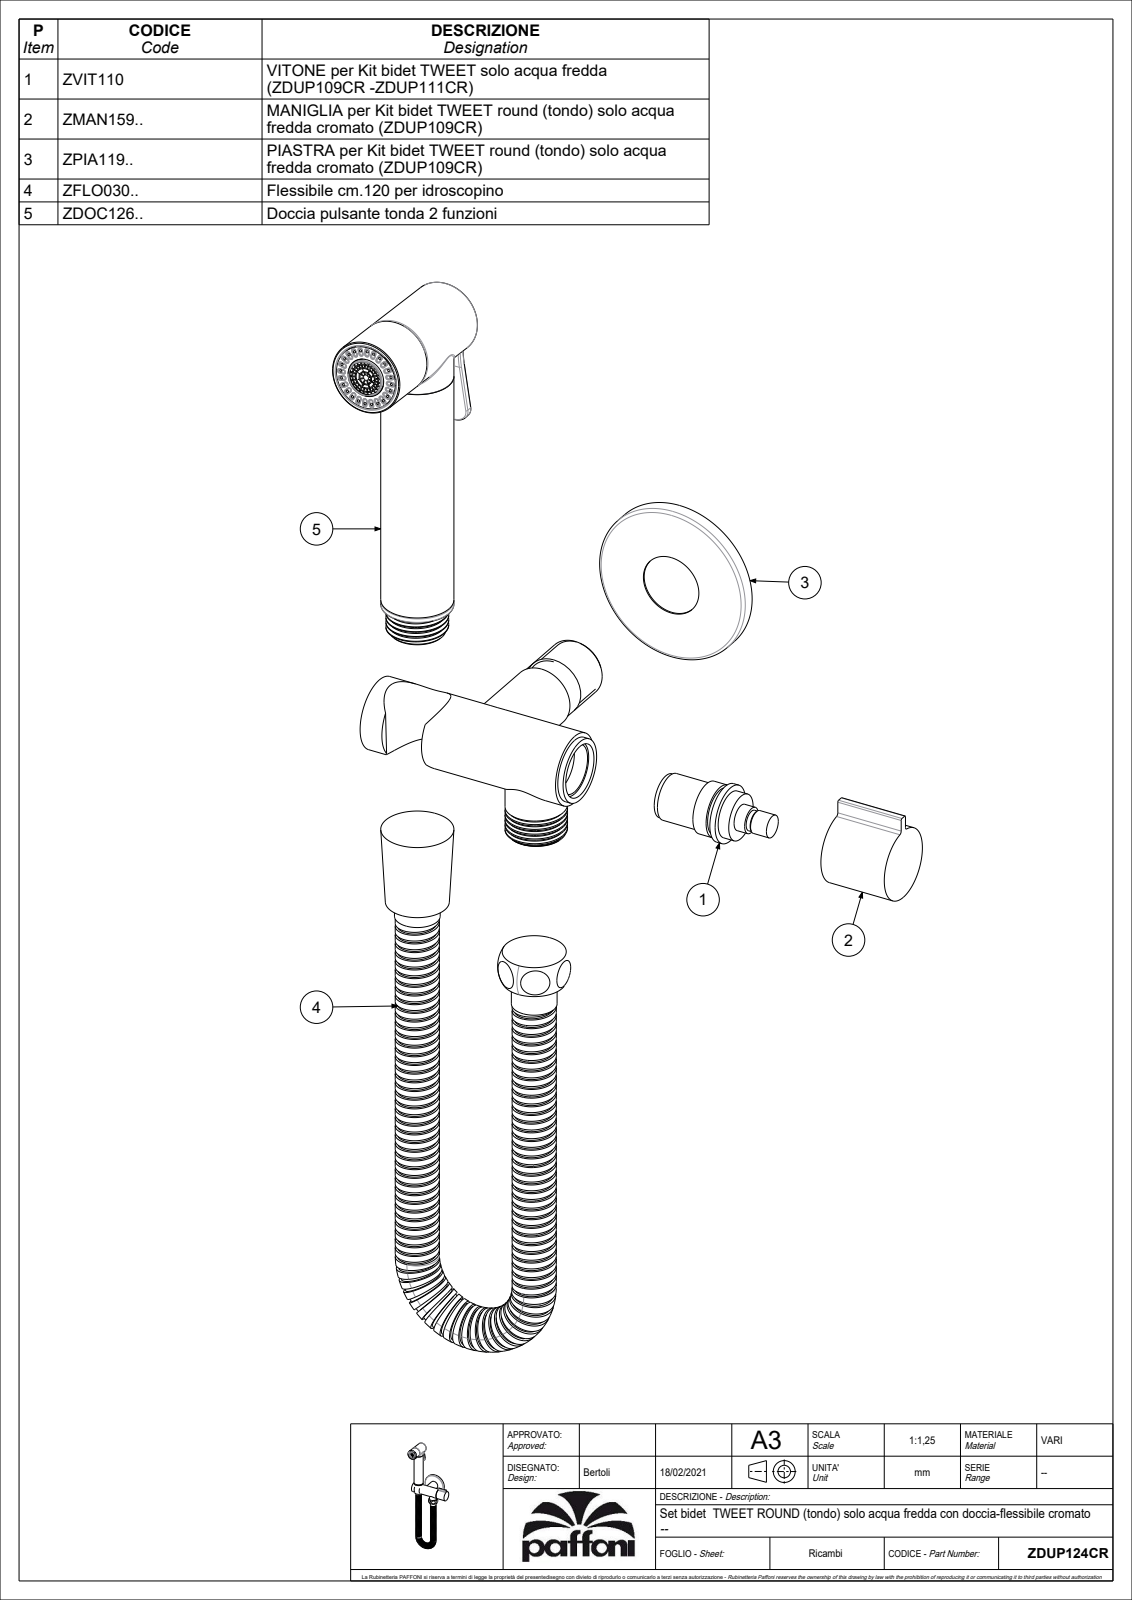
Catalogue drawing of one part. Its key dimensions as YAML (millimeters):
part_name: "ZDUP124CR"
step_written_by: "CREO PARAMETRIC BY PTC INC, 2022124 (CONFIG_CONTROL_DESIGN)"
units: millimeters
bodies: {solids: 0, faces: 760, planar: 153, cylindrical: 266, other: 341}
overall_size: [306.94, 98.5, 80.09]
round_holes:
  - {diameter: 10, count: 1}
  - {diameter: 15.5, count: 1}
  - {diameter: 18.5, count: 1}
  - {diameter: 54, count: 1}
round_bosses_or_shafts:
  - {diameter: 25, count: 2}
  - {diameter: 20.5, count: 2}
  - {diameter: 15, count: 2}
  - {diameter: 14.5, count: 2}
  - {diameter: 55, count: 1}
  - {diameter: 24, count: 1}
  - {diameter: 21.9, count: 1}
  - {diameter: 21.5, count: 1}
partial_cylinders:
  - {radius: 0.2, count: 41}
  - {radius: 0.1, count: 19}
  - {radius: 0.5, count: 8}
  - {radius: 0.3, count: 4}
  - {radius: 1, count: 2}
  - {radius: 30, count: 2}
  - {radius: 6.45, count: 1}
  - {radius: 7.25, count: 1}
face_to_face_distances: [0.5, 98.5, 0.46, 19.06, 18.6, 5, 2.99, 34.99, 35.45, 54.05]
